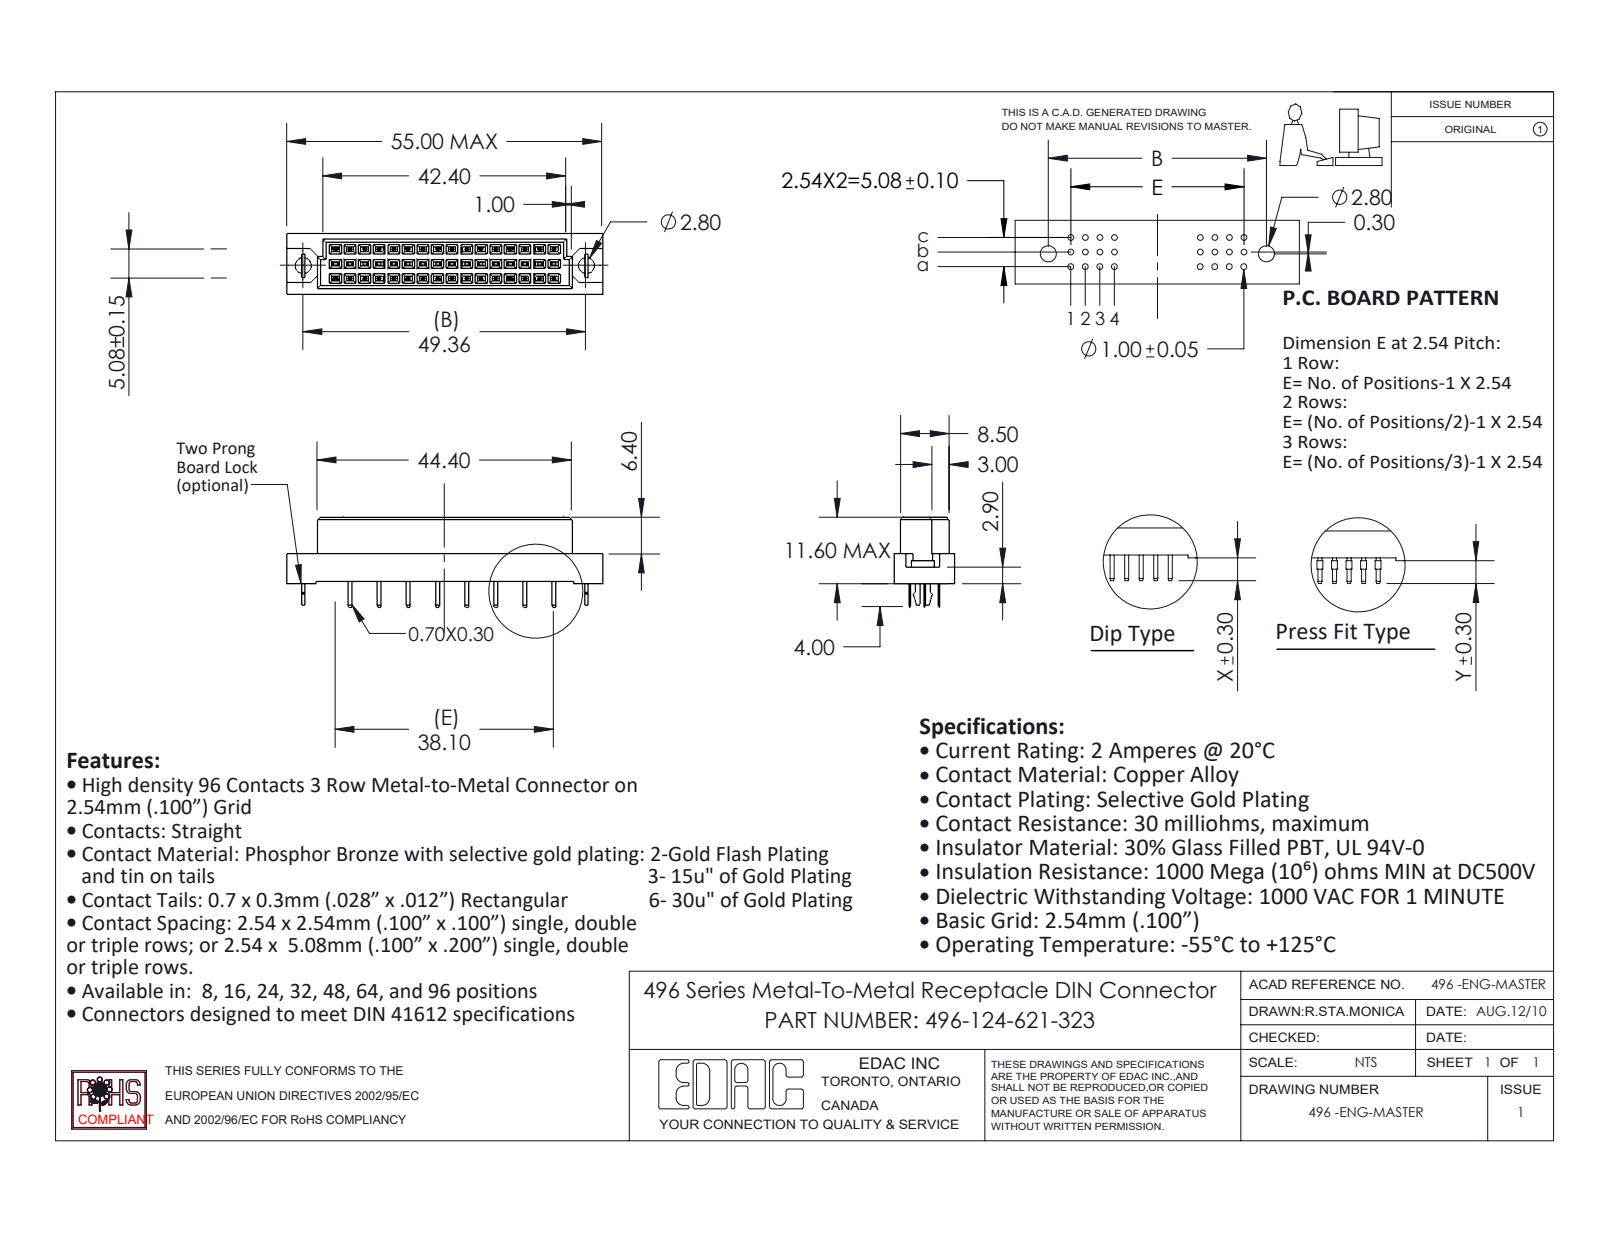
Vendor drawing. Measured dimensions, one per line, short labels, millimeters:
name: 496 Bore-lock; 496-124-621-323; 496 Part_48; 496-290_21
written by: SolidWorks 2020 (CONFIG_CONTROL_DESIGN)
unit: mm
bodies: 27 solids, 942 faces (936 planar, 6 cylindrical, 0 other)
size: 55 × 15.6 × 10.6
volume: 4 654 mm³; area: 4 732 mm²
holes: 2× ⌀2.8
rounds: 1× R0.53
face distances: 2.54, 5.08, 1.05, 9.55, 0.81, 0.56, 0.55, 10.6, 3.35, 1.73
hole spacings: 49.36
